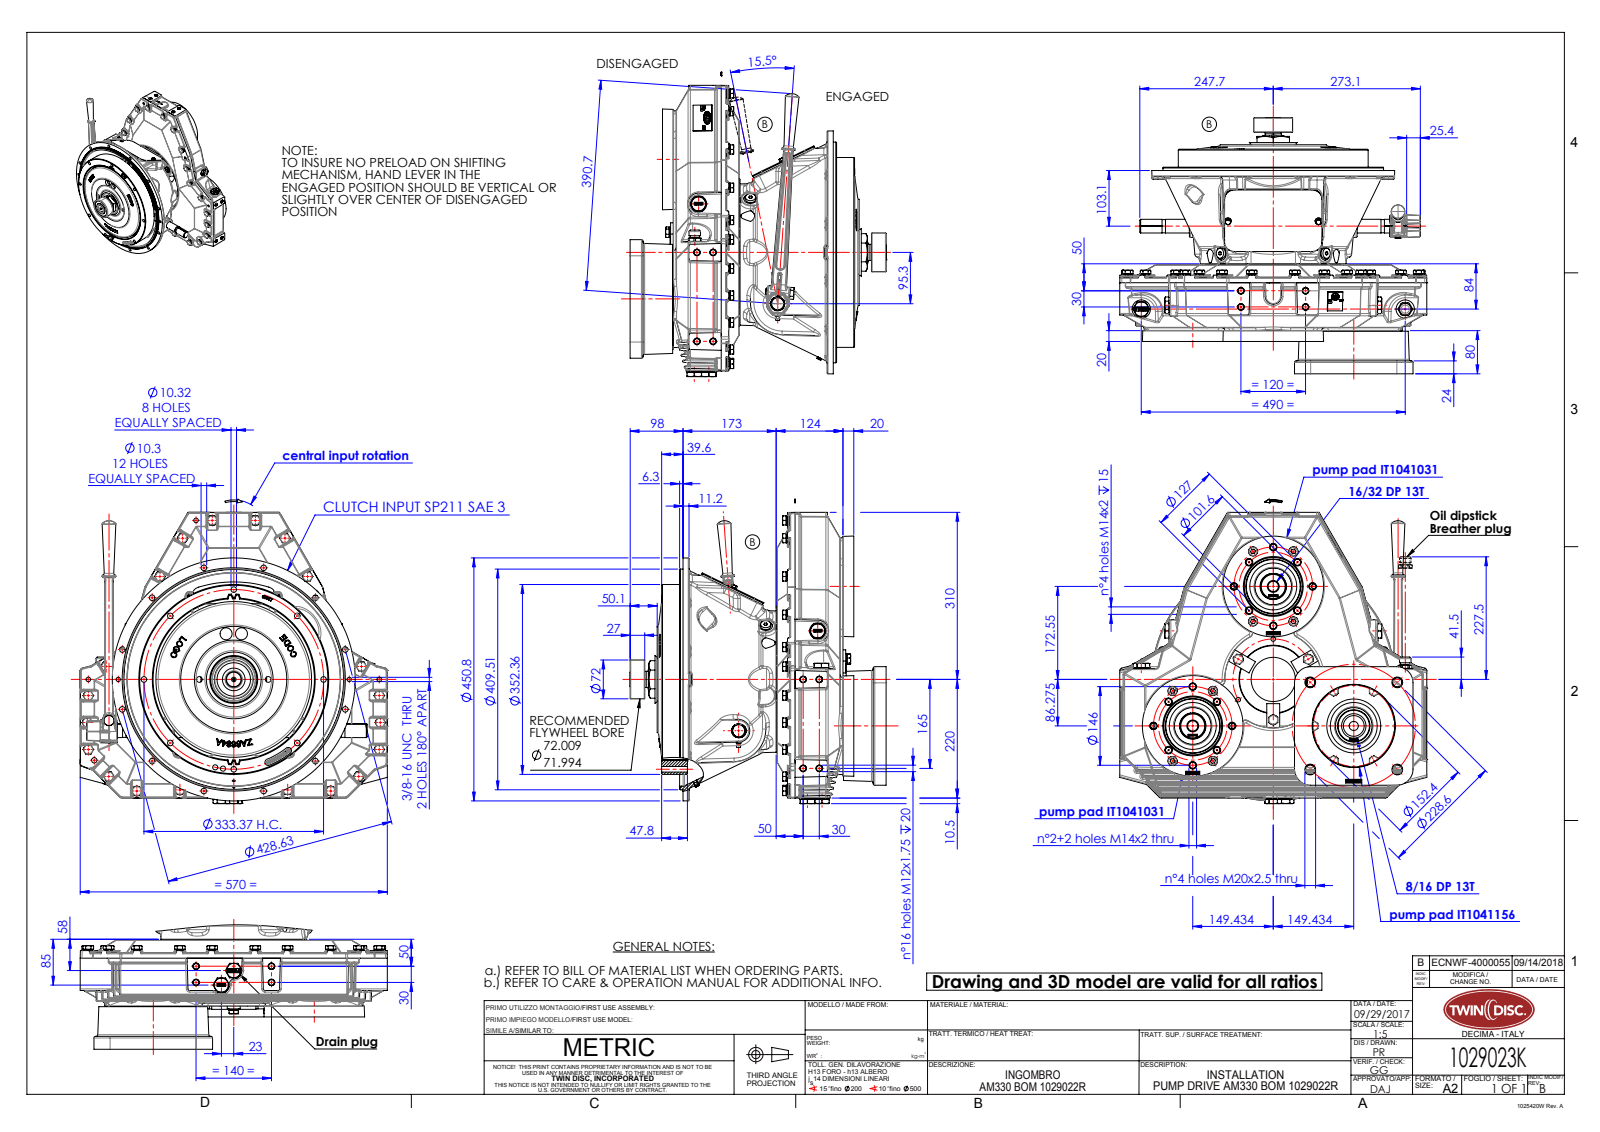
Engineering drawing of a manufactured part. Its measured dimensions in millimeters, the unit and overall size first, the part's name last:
Units: millimetres
Overall size (bounding box): 570 × 565.04 × 475.1
Round holes (diameter × count): ⌀10.2 ×52, ⌀12 ×36, ⌀8.5 ×33, ⌀10.5 ×26, ⌀11 ×16, ⌀10.3 ×12, ⌀10 ×9, ⌀17 ×9, ⌀10.32 ×8, ⌀30 ×8, ⌀13 ×7, ⌀6 ×5
Round bosses / shafts (diameter × count): ⌀10 ×42, ⌀18.1 ×34, ⌀16.2 ×34, ⌀14 ×18, ⌀16 ×8, ⌀20 ×5, ⌀125 ×4, ⌀87.07 ×4
Partial cylindrical surfaces — rounded edges, fillets, slot ends (radius × count): R2 ×352, R0.1 ×224, R3 ×153, R0.25 ×92, R5 ×77, R1.52 ×48, R0.25 ×46, R24.86 ×46
Main face-to-face distances: 89, 11.5, 33, 21.5, 110.5, 122, 144, 85.5, 83.5, 35
Hole centre spacings: 120, 57.4, 75, 138.58, 30, 207.84, 282.91, 10
Volume: 3 713 000 mm³ · Surface area: 3 683 000 mm²
Bodies: 48 solids, 10352 faces (3555 planar, 2686 cylindrical, 4111 other)
Part name (STEP PRODUCT): IT1041156_rev00-installation; ITB00410000_rev01-installation; 1029023K-new; ITam110-013_rev01-installation (+6 more)
STEP written by: SolidWorks 2015 (AUTOMOTIVE_DESIGN)
